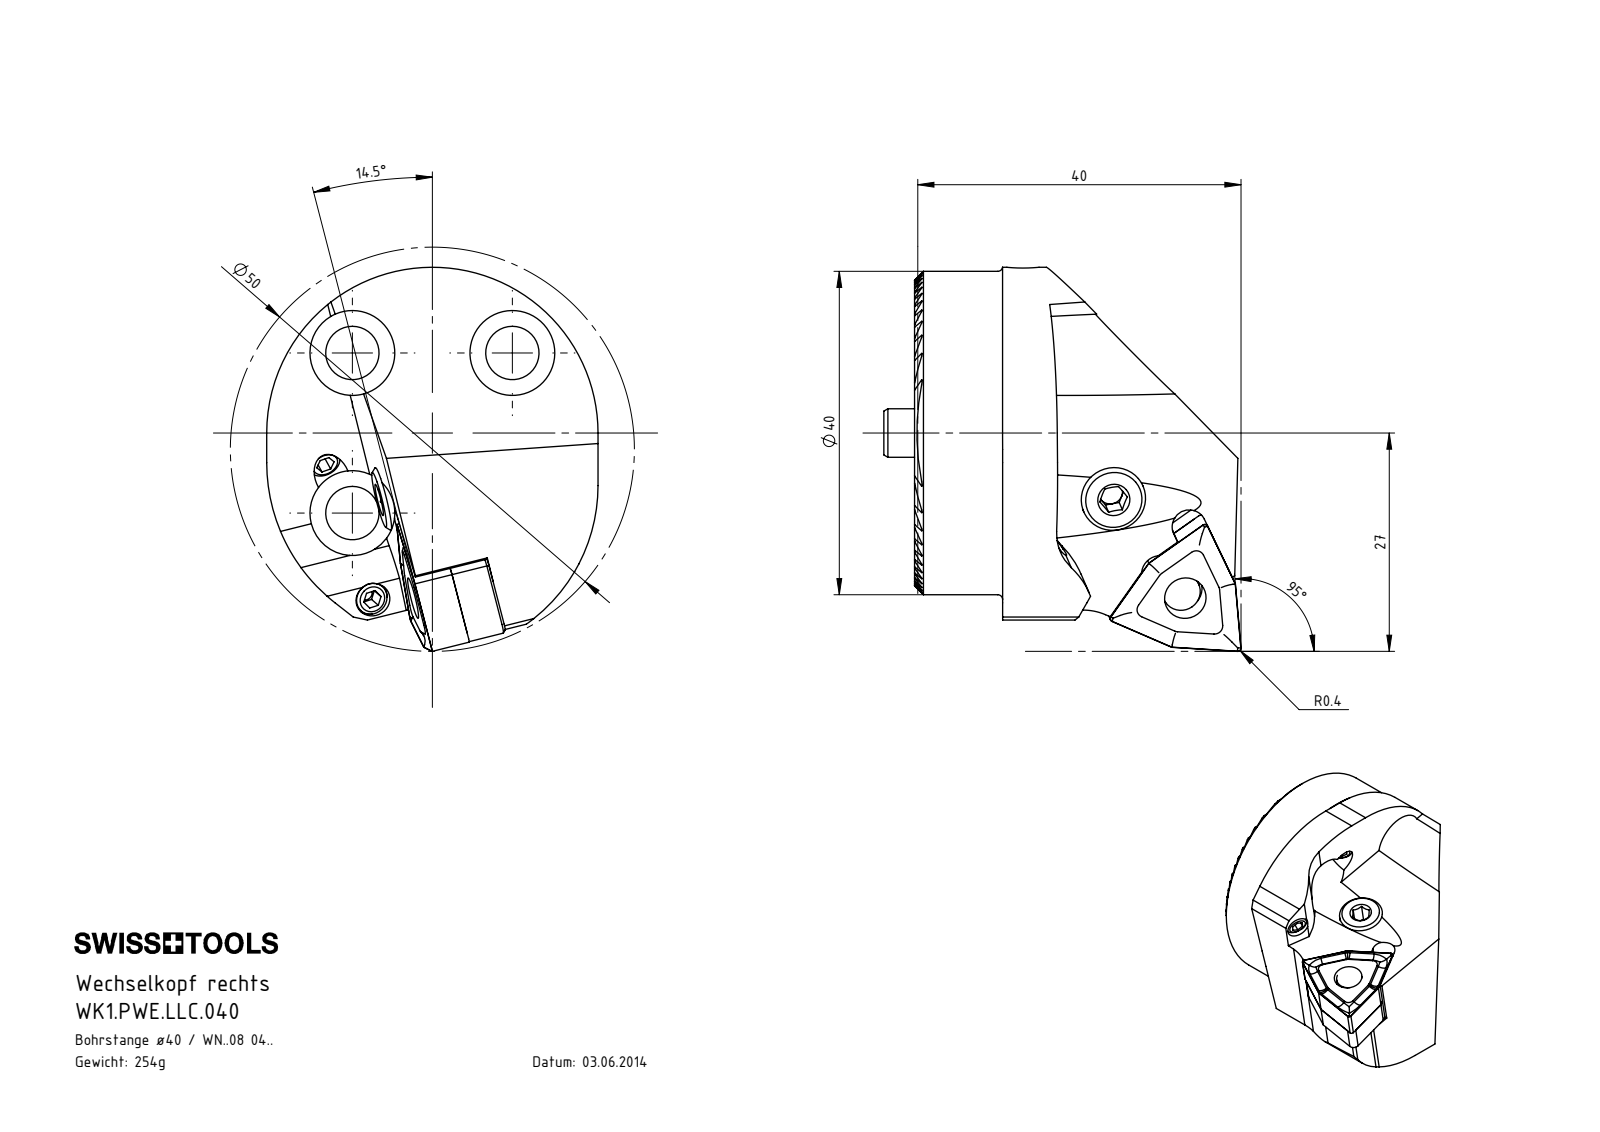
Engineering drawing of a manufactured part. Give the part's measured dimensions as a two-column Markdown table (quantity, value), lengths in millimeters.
| quantity | value |
| --- | --- |
| part name | WK1-PWE.LLC.040_B; KVT_MB_600_040; WKX-ER1.004.005_A_PreviewCfg; WK2-ER1.001.012_A_Fertigbearbeitung (+6 more) |
| STEP written by | SolidWorks 2017 (AUTOMOTIVE_DESIGN) |
| units | millimeters |
| bodies | 15 solids, 690 faces (276 planar, 220 cylindrical, 194 other) |
| overall size | 47.51 × 44.2 × 41 |
| volume | 31 773 mm³ |
| surface area | 15 041 mm² |
| round holes (diameter × count) | 3.3 × 5, 3 × 3, 4.2 × 3, 6.6 × 3, 10.5 × 3, 1.7 × 2, 4 × 2, 5.16 × 1, 6.4 × 1, 6.7 × 1, 7 × 1, 7.8 × 1 |
| round bosses / shafts (diameter × count) | 4 × 5, 40 × 1, 8 × 1, 7.9 × 1, 6.4 × 1, 6 × 1, 4.7 × 1, 3.55 × 1 |
| partial cylindrical surfaces (radius × count) | 0.12 × 26, 0.4 × 3, 1 × 3, 2.5 × 3, 7 × 2, 2.1 × 1, 2.3 × 1, 2.35 × 1 |
| main face-to-face distances | 1.3, 2.6, 3.9, 12.99, 5.2, 11.69, 9.09, 10.39, 7.79, 6.5 |
| hole center spacings | 14, 15.61, 19.8, 15.6, 28 |
